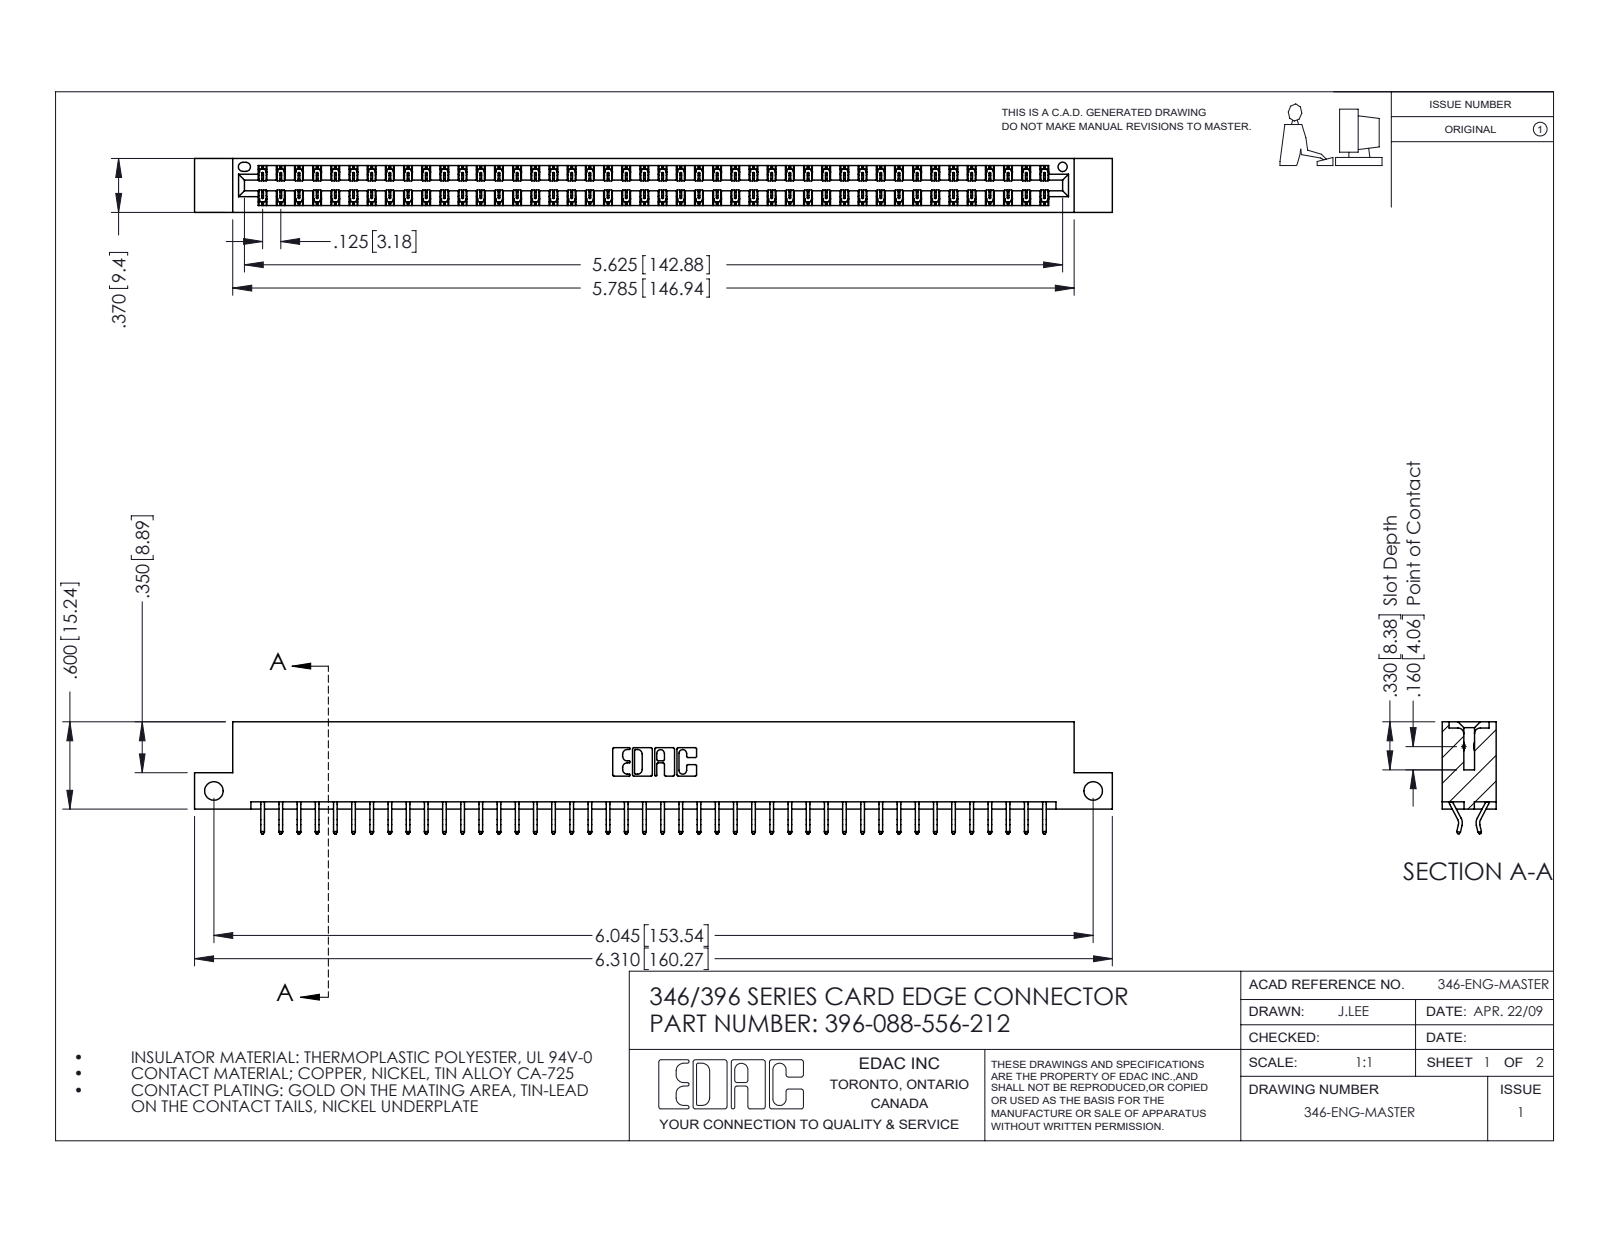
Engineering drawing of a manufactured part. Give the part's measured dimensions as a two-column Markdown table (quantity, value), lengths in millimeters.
| quantity | value |
| --- | --- |
| part name | 396-088-556-212; 345-292-001_556 Tail; 346 Part_Flush Mounting Lugs - Side Mount |
| STEP written by | SolidWorks 2016 (CONFIG_CONTROL_DESIGN) |
| units | millimeters |
| bodies | 89 solids, 5226 faces (3508 planar, 1718 cylindrical, 0 other) |
| overall size | 160.3 × 19.6 × 9.4 |
| volume | 15 600 mm³ |
| surface area | 21 190 mm² |
| round holes (diameter × count) | 3.3 × 2, 1.6 × 1 |
| partial cylindrical surfaces (radius × count) | 0.2 × 132, 0.3 × 22, 0.2 × 6, 0.8 × 6, 0.7 × 3, 0.3 × 2, 0.4 × 2, 0.6 × 2 |
| main face-to-face distances | 1.2, 8.2, 9.4, 6.4, 0.6, 1.8, 7.6, 7, 3.8, 5.6 |
| hole center spacings | 153.5 |
